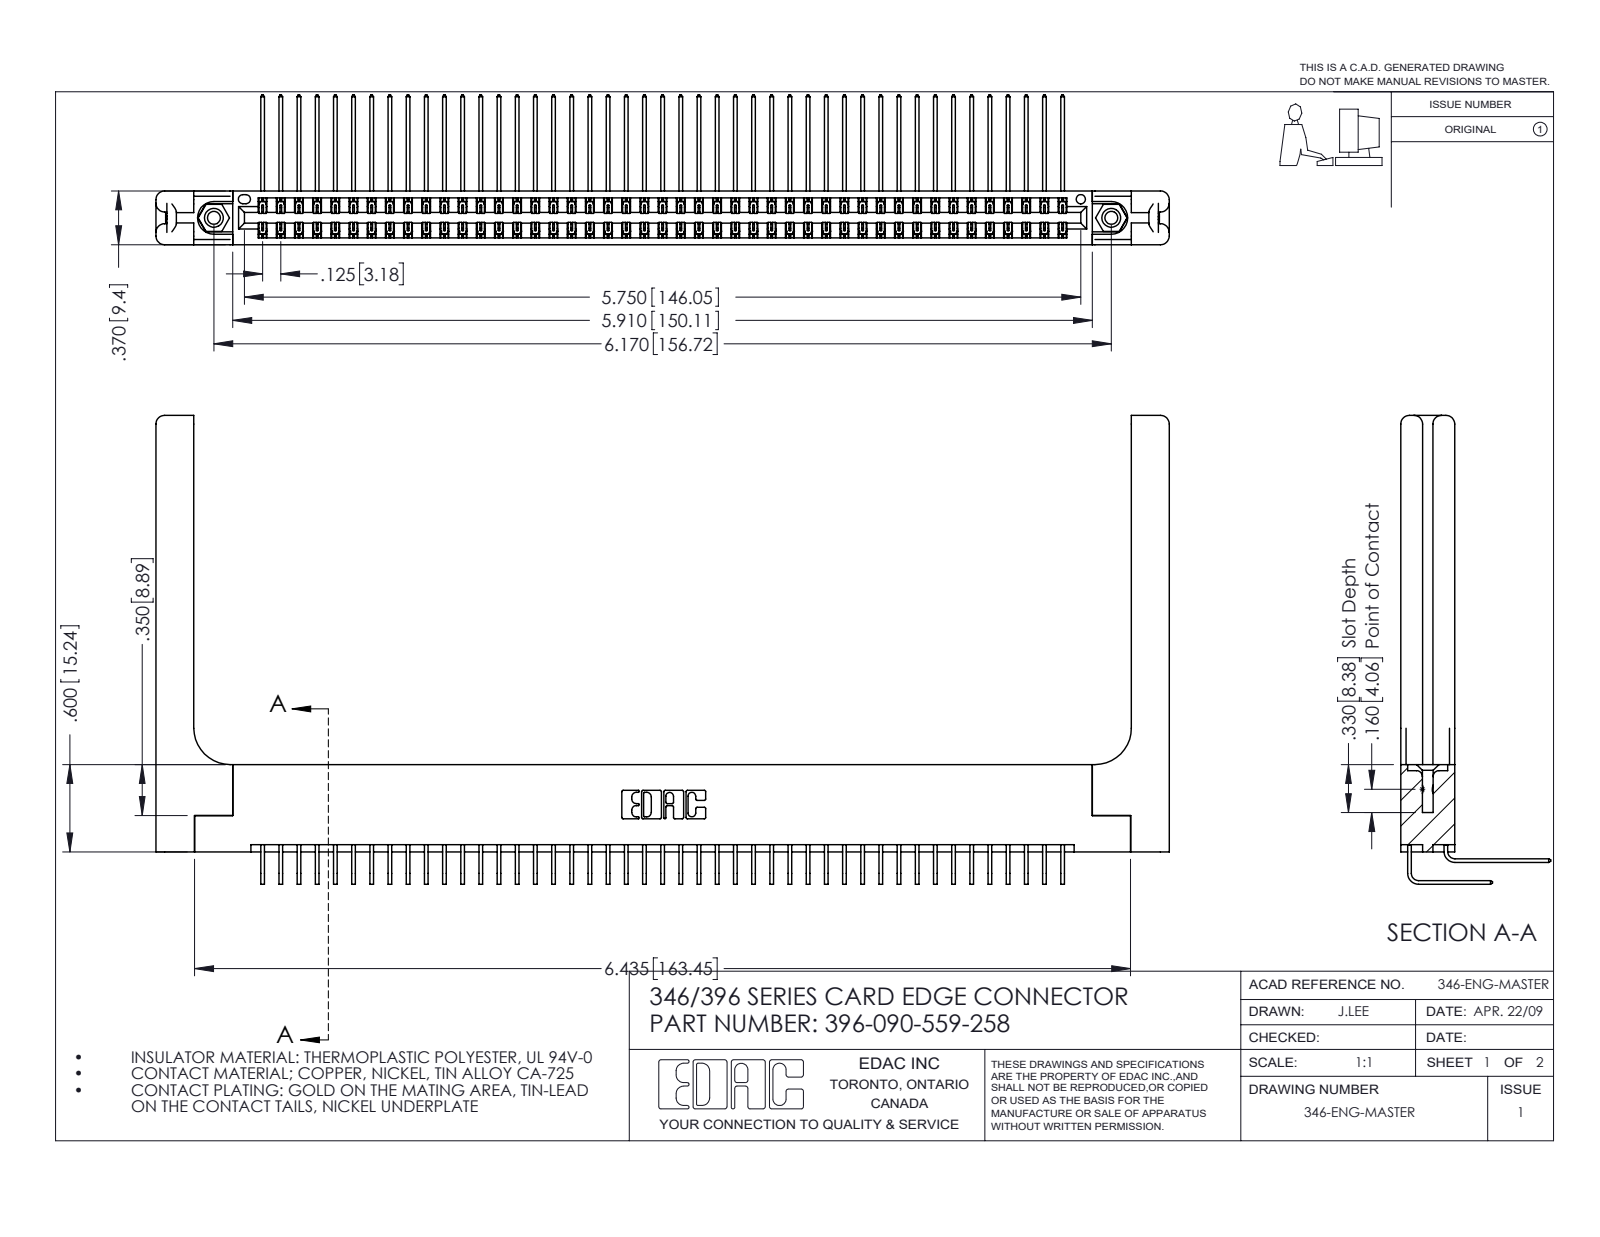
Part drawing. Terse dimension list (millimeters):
name: 346-220-058_345-220-058; 345-250-001_345-250-001-102; 345-292-001_558 559 Tail - 1; 396-090-559-258 (+2 more)
written by: SolidWorks 2016 (CONFIG_CONTROL_DESIGN)
unit: mm
bodies: 95 solids, 5238 faces (3554 planar, 1624 cylindrical, 60 other)
size: 176.9 × 81.9 × 26.2
volume: 25 290 mm³; area: 31 970 mm²
holes: 2× ⌀2.3, 2× ⌀3.2, 2× ⌀4, 1× ⌀1.6
bosses: 2× ⌀3.9
rounds: 135× R0.2, 22× R0.3, 16× R1.5, 6× R0.2, 6× R0.8, 3× R0.7, 2× R0.4, 2× R0.6
face distances: 1.2, 8.2, 9.4, 1.8, 0.6, 6.4, 3.8, 3.8, 7.6, 7
hole spacings: 6.2, 151.4, 156.7
